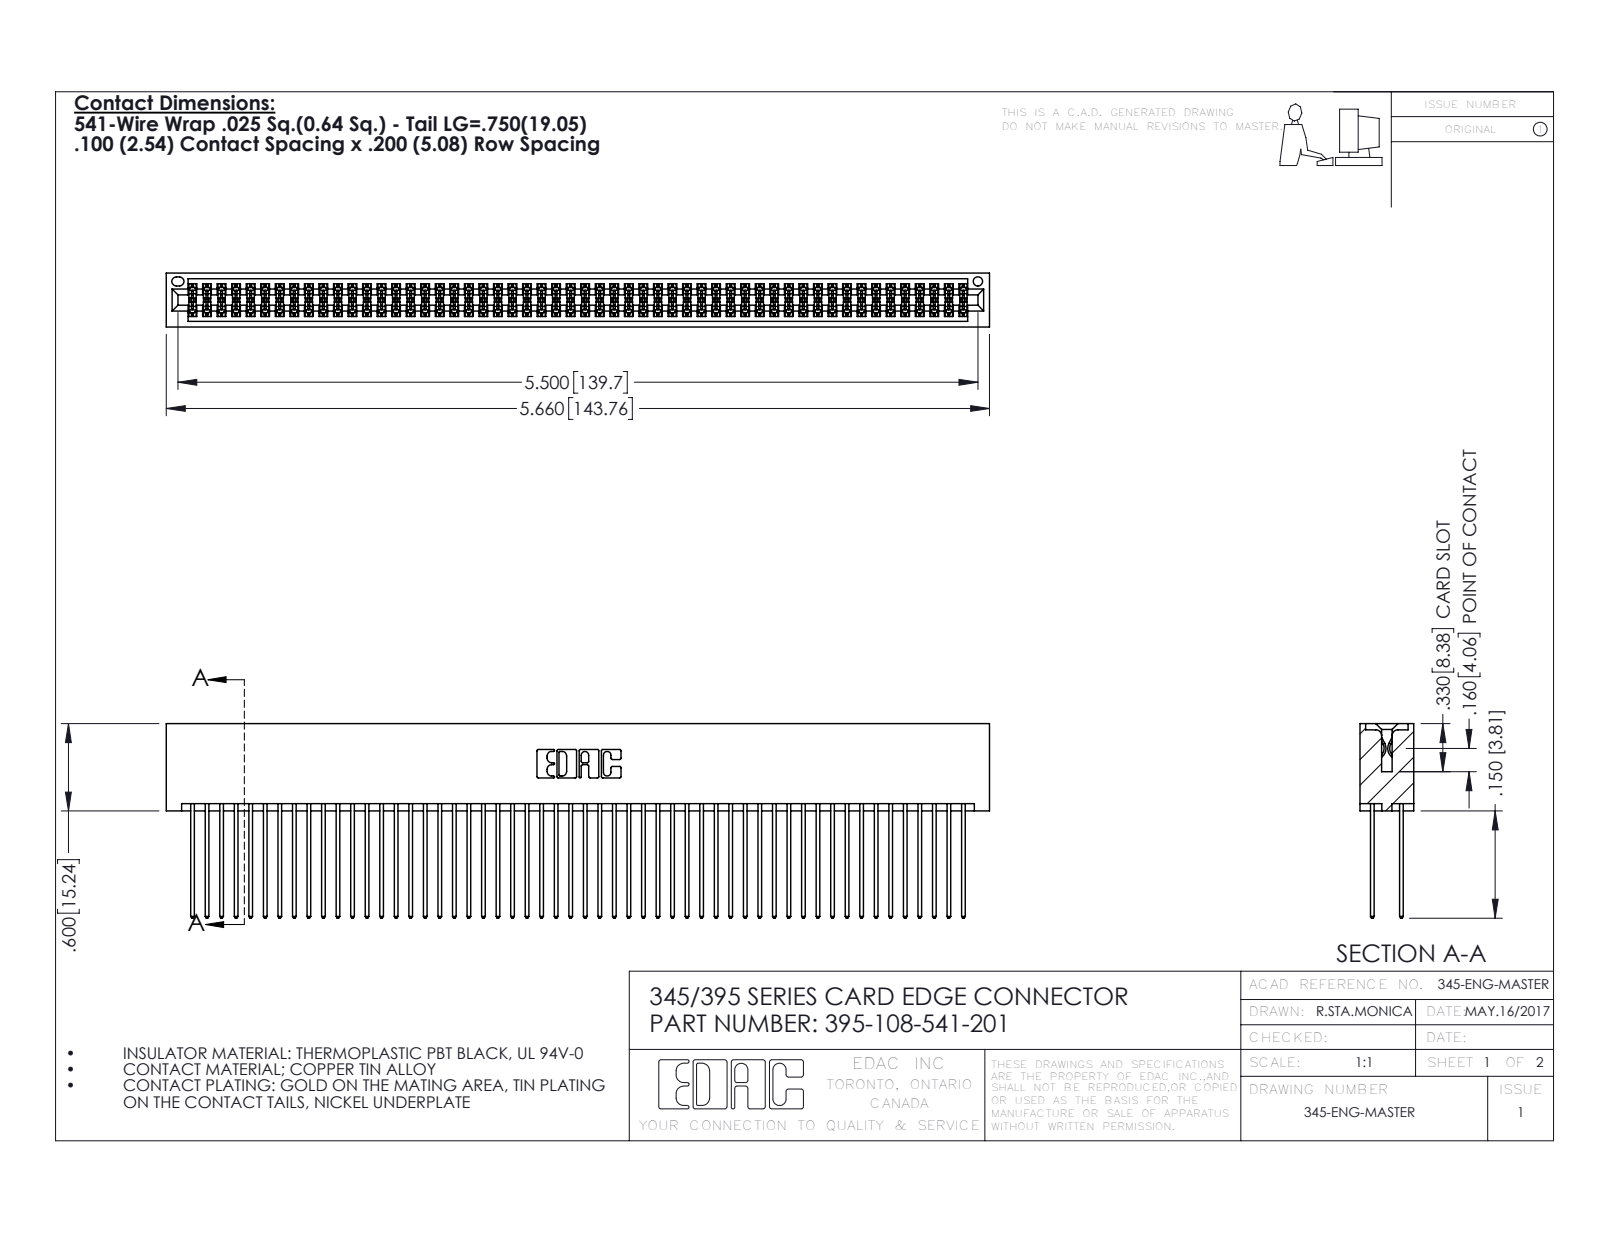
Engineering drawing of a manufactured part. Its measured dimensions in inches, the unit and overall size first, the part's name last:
Units: inches
Overall size (bounding box): 5.66 × 1.337 × 0.37
Round holes (diameter × count): ⌀0.064 ×1
Partial cylindrical surfaces — rounded edges, fillets, slot ends (radius × count): R0.006 ×162, R0.01 ×108, R0.01 ×22, R0.007 ×6, R0.031 ×6, R0.026 ×3, R0.014 ×2, R0.019 ×2
Main face-to-face distances: 0.298, 0.072, 0.2, 0.098, 0.272, 0.025, 0.225, 0.37, 0.175, 0.149
Volume: 0.934 in³ · Surface area: 40.43 in²
Bodies: 109 solids, 5518 faces (3640 planar, 1878 cylindrical, 0 other)
Part name (STEP PRODUCT): 345-292-001_345-293-141; 395-108-541-201; 345 Part_No Mounting Lugs
STEP written by: SolidWorks 2016 (CONFIG_CONTROL_DESIGN)
